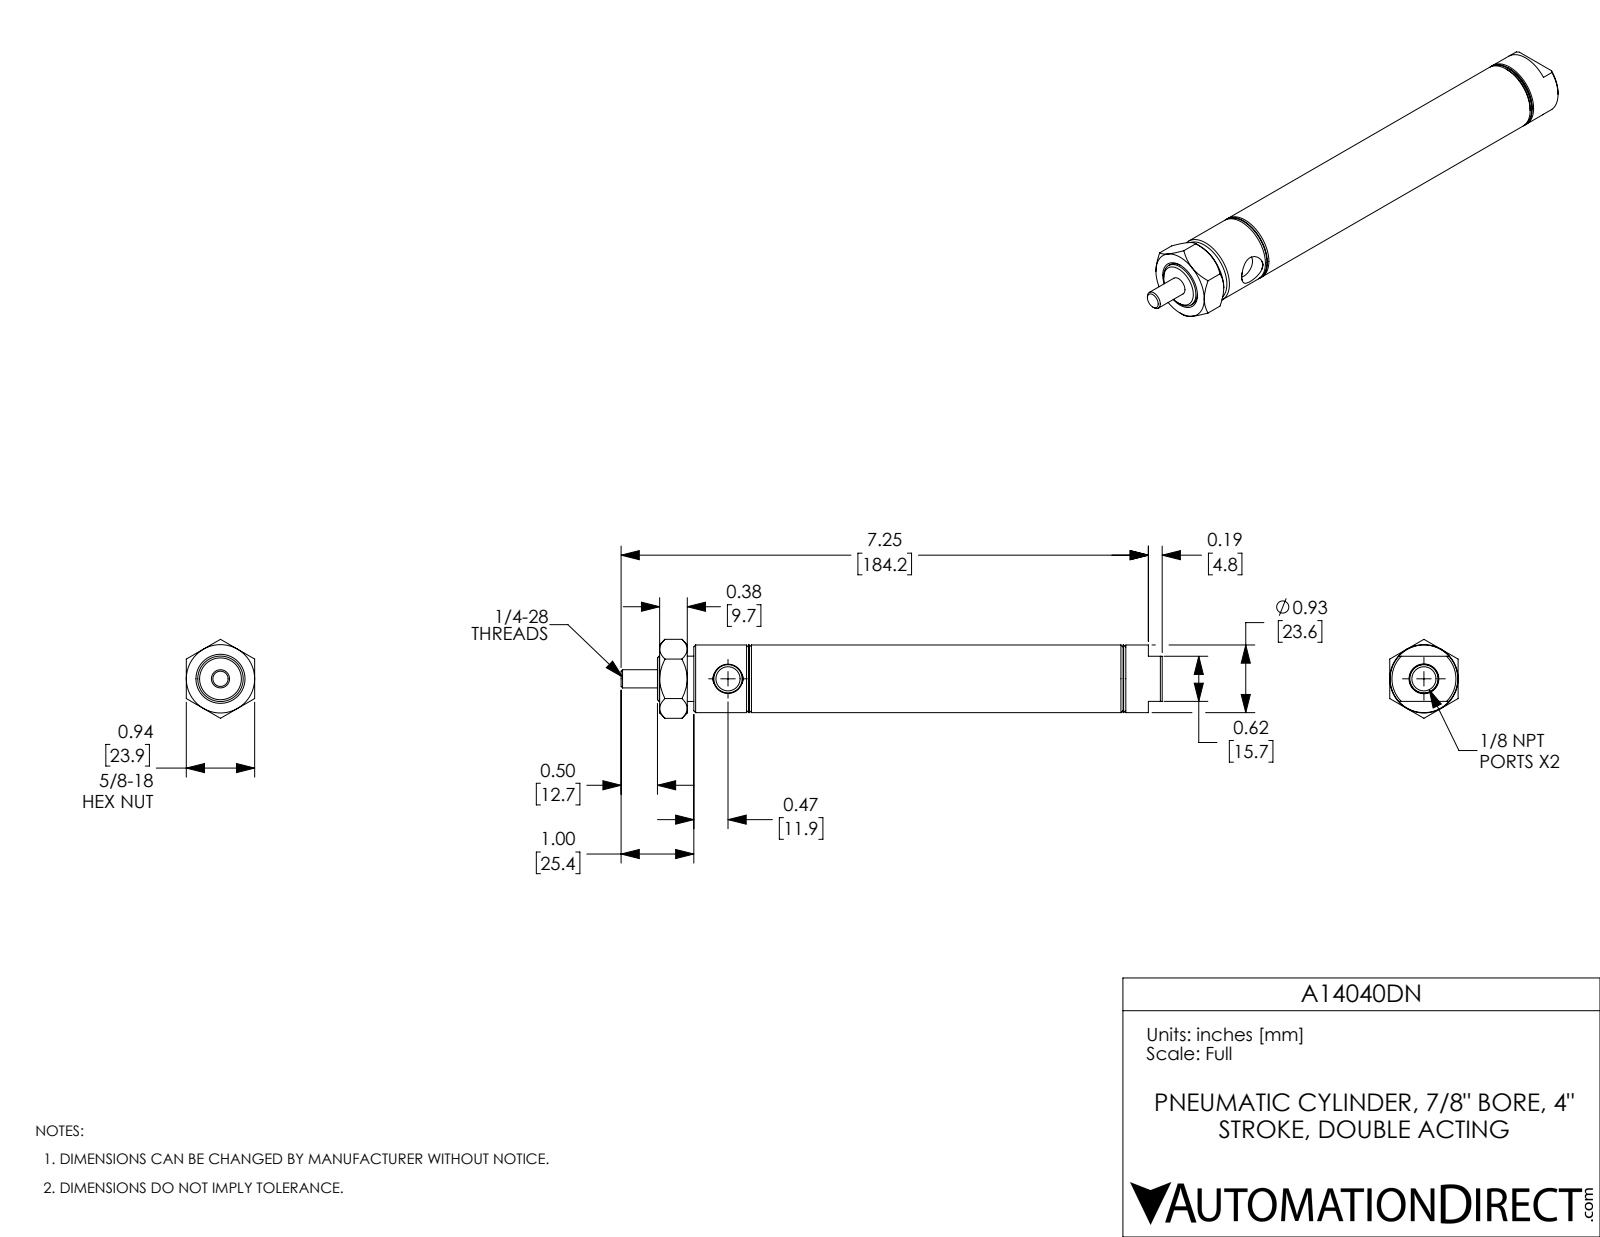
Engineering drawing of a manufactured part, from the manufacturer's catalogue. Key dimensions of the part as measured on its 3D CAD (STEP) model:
Part name (STEP PRODUCT): A14040DN_Main Body; A14040DN_Rod; A14040DN_Mounting Nut_D-9; A14040DN
STEP written by: SolidWorks 2017 (AUTOMOTIVE_DESIGN)
Units: inches
Bodies: 3 solids, 104 faces (28 planar, 30 cylindrical, 46 other)
Overall size (bounding box): 7.44 × 1.085 × 0.94
Volume: 2.427 in³ · Surface area: 47.04 in²
Round holes (diameter × count): ⌀0.25 ×1, ⌀0.332 ×1, ⌀0.625 ×1, ⌀0.875 ×1
Round bosses / shafts (diameter × count): ⌀0.93 ×1, ⌀0.623 ×1, ⌀0.562 ×1, ⌀0.332 ×1
Main face-to-face distances: 0.5, 4.5, 4, 0.94, 5.583, 0.857, 5.673, 5.173, 1.173, 6.44
